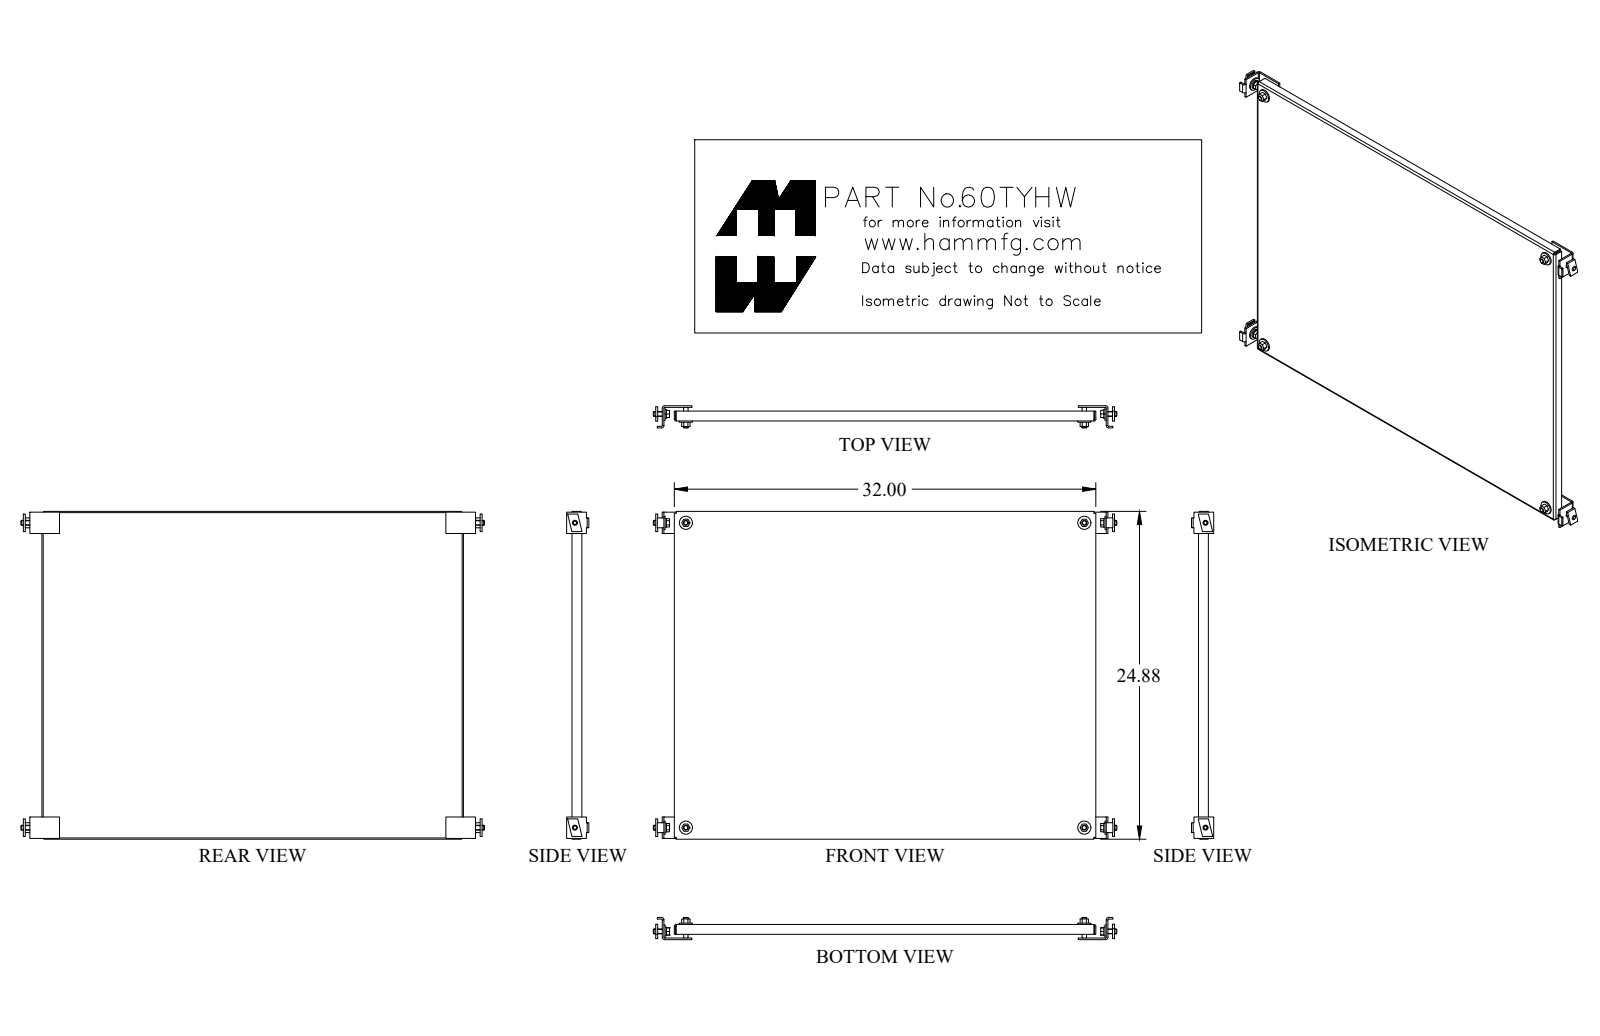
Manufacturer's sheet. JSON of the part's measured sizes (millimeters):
{"part_name": "60TYHW_Default", "step_written_by": "SolidWorks 2018 (CONFIG_CONTROL_DESIGN)", "units": "millimeters", "bodies": {"solids": 1, "faces": 38, "planar": 22, "cylindrical": 16, "other": 0}, "overall_size": [812.8, 631.8, 19.1], "volume_mm3": 1345000, "surface_area_mm2": 1123000, "round_holes": [[14.3, 4]], "partial_cylinders_radius": [[1.2, 4], [3.6, 4]], "face_to_face_distances": [2.4, 629.4, 810.4, 631.8, 627, 812.8, 808, 19.1, 16.6, 3.6], "hole_center_spacings": [587.4, 768.4, 967.2]}
